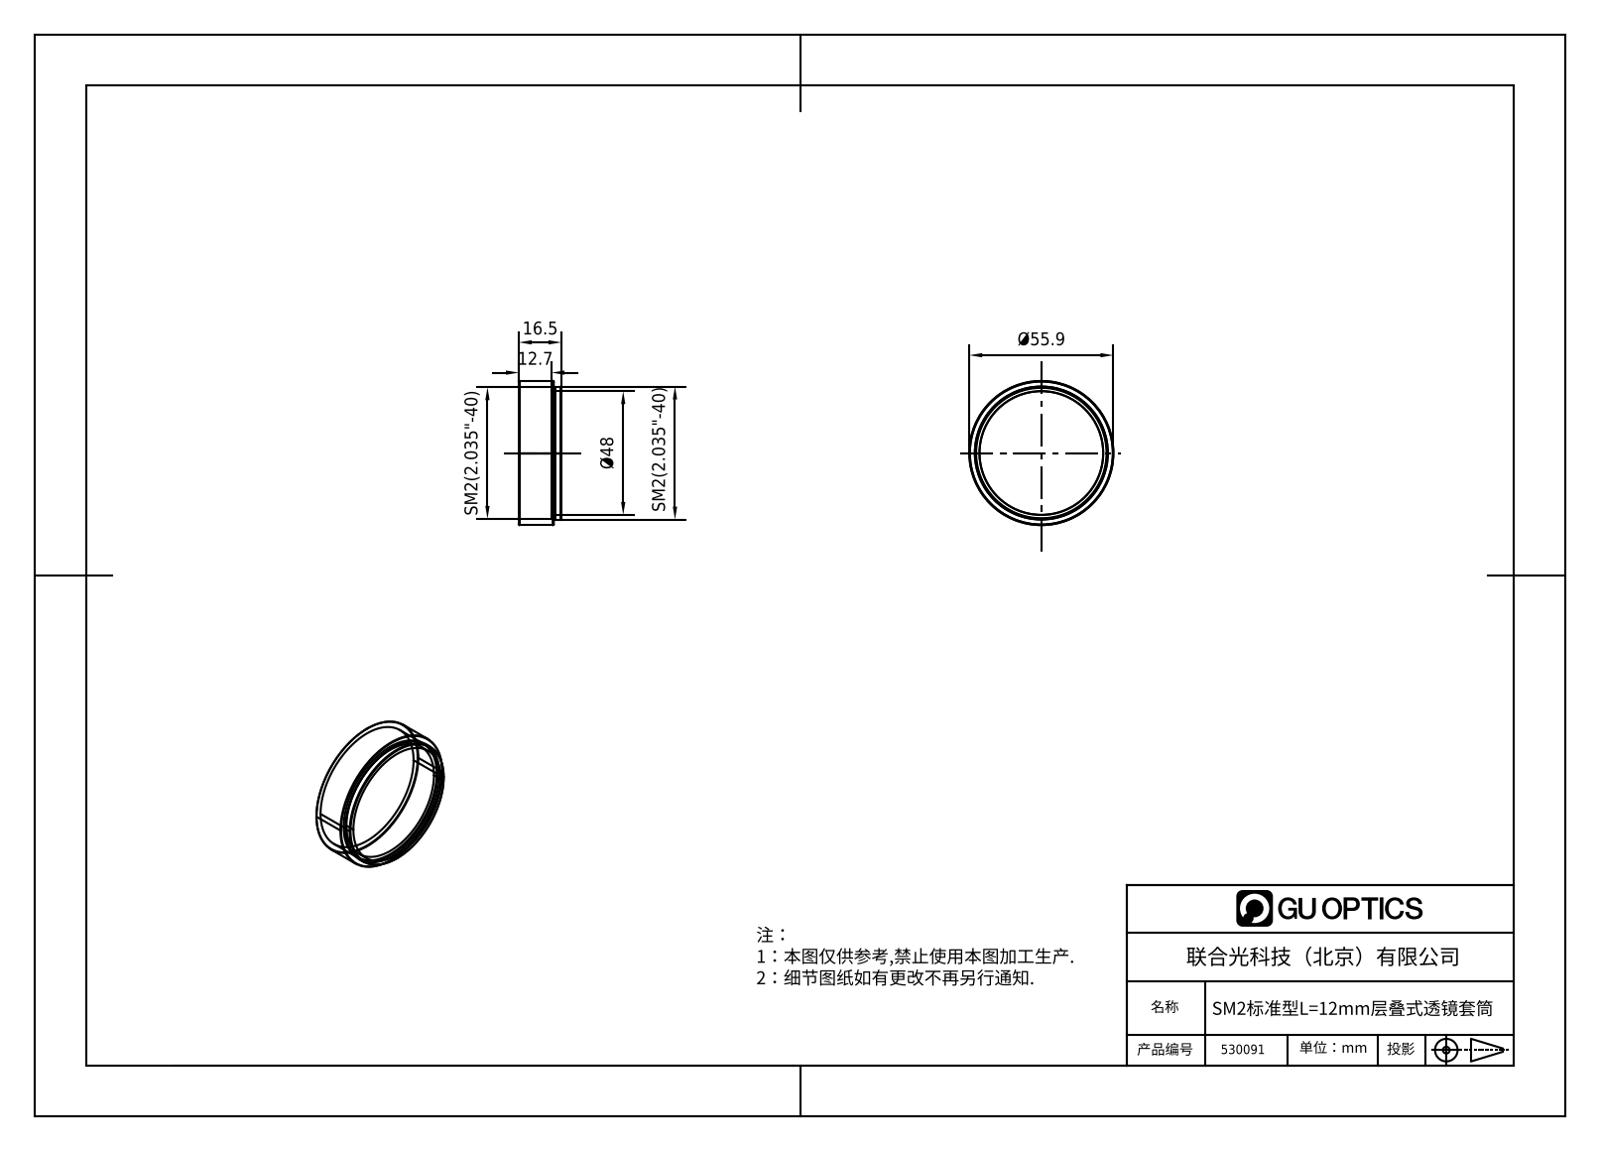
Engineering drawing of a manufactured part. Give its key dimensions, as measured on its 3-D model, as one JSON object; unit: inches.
{"part_name": "1.7.1.17_ZTC-2-0.5_SM2标准型0.5英寸层叠式透镜套筒", "step_written_by": "SolidWorks 2018 (AUTOMOTIVE_DESIGN)", "units": "inches", "bodies": {"solids": 0, "faces": 36, "planar": 13, "cylindrical": 12, "other": 11}, "overall_size": [2.201, 2.201, 0.65], "round_holes": [[1.878, 1], [1.89, 1], [2.01, 1]], "round_bosses_or_shafts": [[2.201, 1], [2.031, 1], [1.992, 1]], "face_to_face_distances": [0.531, 0.65, 0.118, 0.5, 0.031, 0.15, 0.152, 0.348, 0.38, 0.498]}
